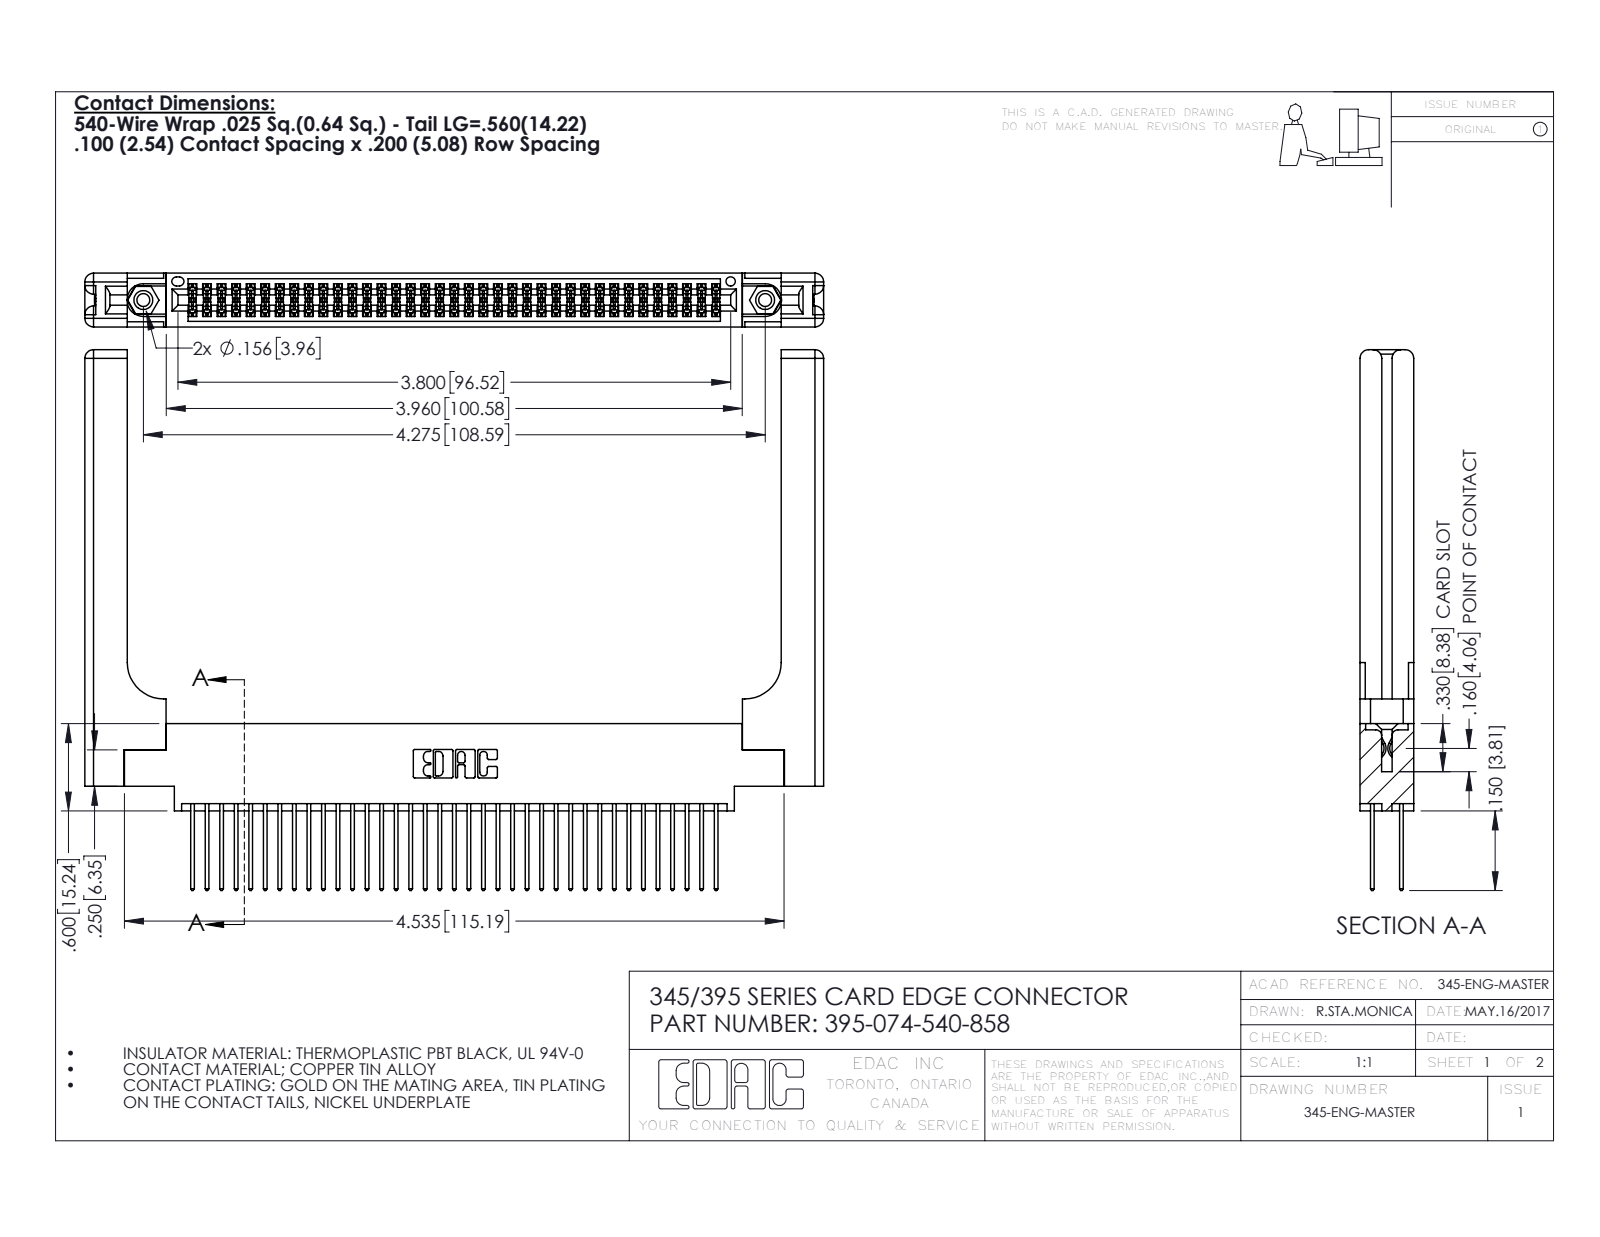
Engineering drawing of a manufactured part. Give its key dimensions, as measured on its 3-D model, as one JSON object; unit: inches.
{"part_name": "345 Part_0.170 Offset - 0.156 Dia-TH; 345-220-058_345-220-058; 395-074-540-858; 345-250-001_345-250-001-102 (+1 more)", "step_written_by": "SolidWorks 2016 (CONFIG_CONTROL_DESIGN)", "units": "inches", "bodies": {"solids": 79, "faces": 4086, "planar": 2674, "cylindrical": 1352, "other": 60}, "overall_size": [5.079, 3.717, 0.37], "volume_in3": 1.289, "surface_area_in2": 38.92, "round_holes": [[0.089, 2], [0.125, 2], [0.156, 2], [0.064, 1]], "round_bosses_or_shafts": [[0.155, 2]], "partial_cylinders_radius": [[0.006, 111], [0.01, 74], [0.01, 22], [0.06, 16], [0.007, 6], [0.031, 6], [0.026, 3], [0.014, 2]], "face_to_face_distances": [0.072, 0.298, 0.37, 0.098, 0.272, 0.025, 0.2, 0.225, 0.175, 0.148], "hole_center_spacings": [0.27, 4.039, 4.275]}
